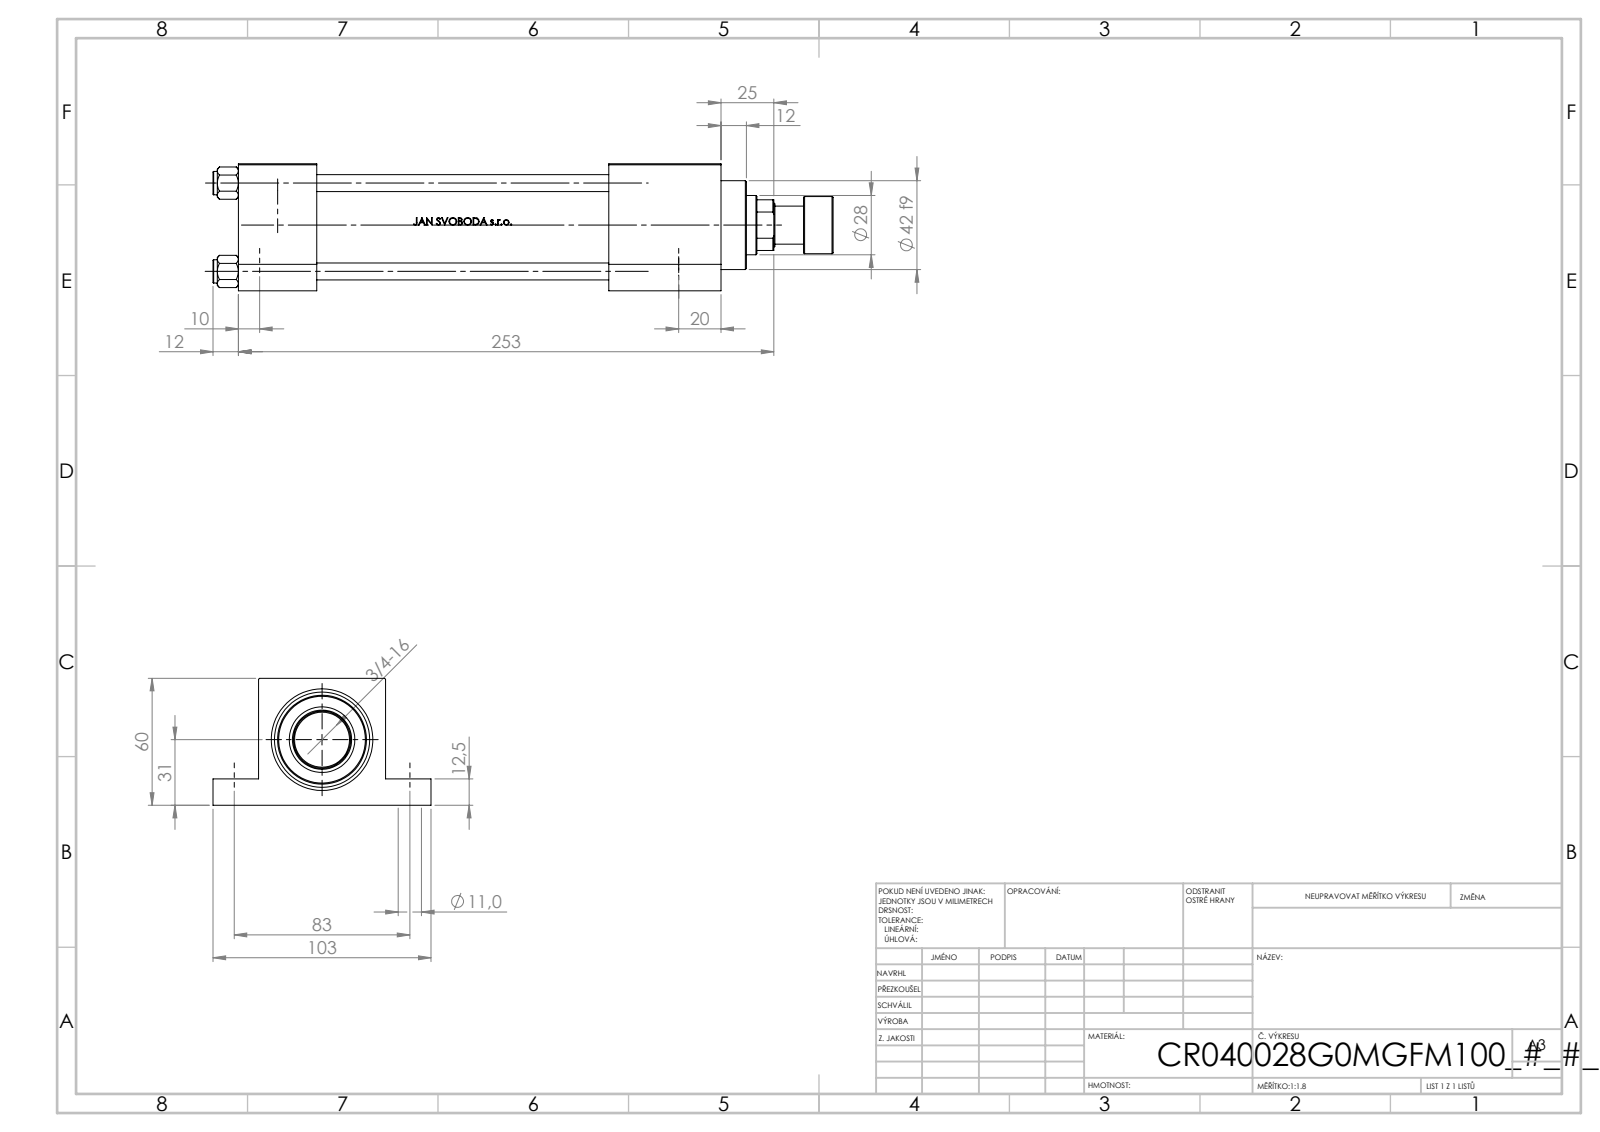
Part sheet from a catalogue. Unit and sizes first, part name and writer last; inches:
Units: inches
Overall size (bounding box): 11.535 × 4.055 × 2.362
Round holes (diameter × count): ⌀0.315 ×4, ⌀0.433 ×4, ⌀0.276 ×2, ⌀0.656 ×2, ⌀0.945 ×2, ⌀0.728 ×1, ⌀1.102 ×1, ⌀1.22 ×1, ⌀1.575 ×1, ⌀1.772 ×1
Round bosses / shafts (diameter × count): ⌀0.433 ×4, ⌀1.811 ×1, ⌀1.654 ×1, ⌀1.063 ×1, ⌀0.709 ×1
Main face-to-face distances: 2.362, 1.457, 0.492, 1.87, 2.087, 6.89, 5.433, 8.976, 7.52, 0.846
Hole centre spacings: 1.642, 1.133, 1.189, 1.668, 1.766, 2.322, 3.268, 7.311
Volume: 35.49 in³ · Surface area: 248.2 in²
Bodies: 12 solids, 1104 faces (436 planar, 130 cylindrical, 538 other)
Part name (STEP PRODUCT): V215CR_ROD_END_F; V215_VC_A; NUT_M5_G; V215CR_G_Body (+2 more)
STEP written by: SolidWorks 2019 (CONFIG_CONTROL_DESIGN)
